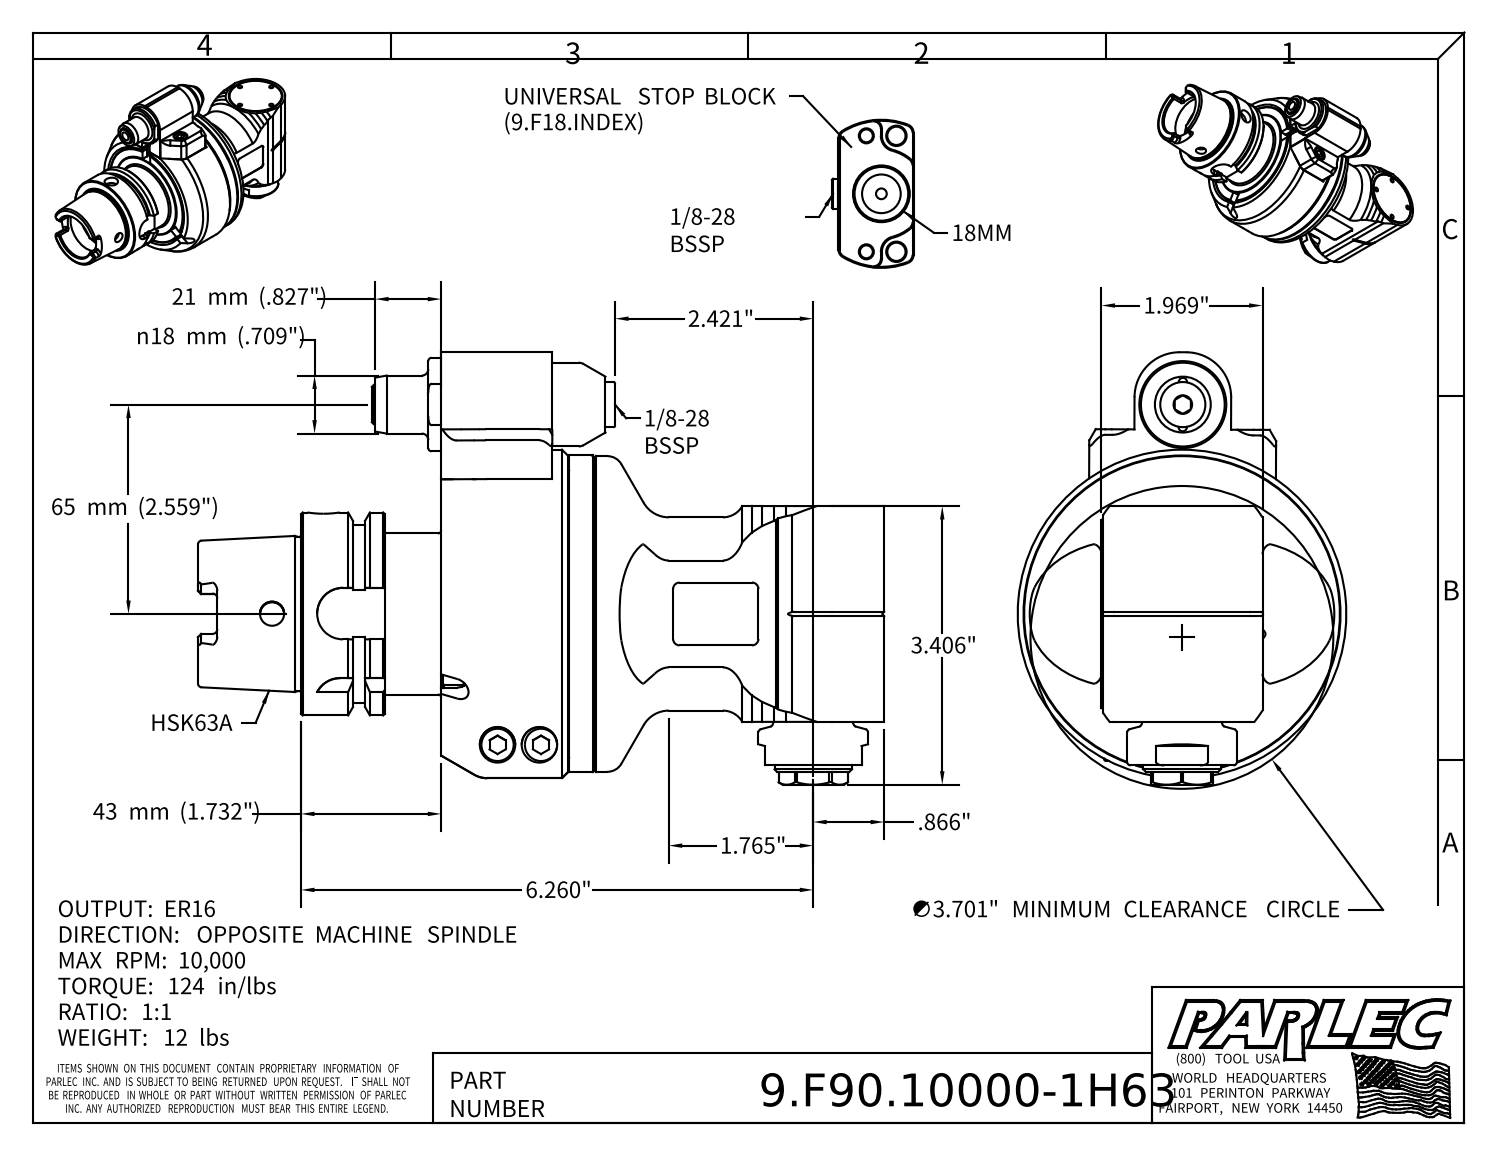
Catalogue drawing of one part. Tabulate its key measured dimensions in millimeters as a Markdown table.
| quantity | value |
| --- | --- |
| part name | 9.F90.10000-1H63; 9.F90.10000; 9_GA1_566_2_1_H63; 9FL1ATC (+4 more) |
| STEP written by | Autodesk Inventor 2022 (AUTOMOTIVE_DESIGN) |
| units | millimeters |
| bodies | 5 solids, 608 faces (266 planar, 160 cylindrical, 182 other) |
| overall size | 213 × 134.3 × 102 |
| volume | 814 800 mm³ |
| surface area | 143 000 mm² |
| round holes (diameter × count) | 8.5 × 20, 3.2 × 4, 11 × 3, 2.6 × 2, 4.2 × 2, 5 × 2, 10.4 × 2, 12.5 × 2, 2.5 × 1, 3 × 1, 6.5 × 1, 7 × 1 |
| round bosses / shafts (diameter × count) | 10 × 4, 6 × 4, 18 × 2, 8 × 2, 2.5 × 2, 102 × 1, 98.4 × 1, 98 × 1 |
| partial cylindrical surfaces (radius × count) | 2 × 12, 1.5 × 6, 2.9 × 4, 4 × 4, 8 × 4, 0.4 × 2, 0.5 × 2, 1 × 2 |
| main face-to-face distances | 32, 26, 0.5, 7, 39.5, 7.5, 8.5, 34, 52, 5 |
| hole center spacings | 38.5, 54.5, 46.3, 76.3, 21.2, 67.3, 74, 77 |
